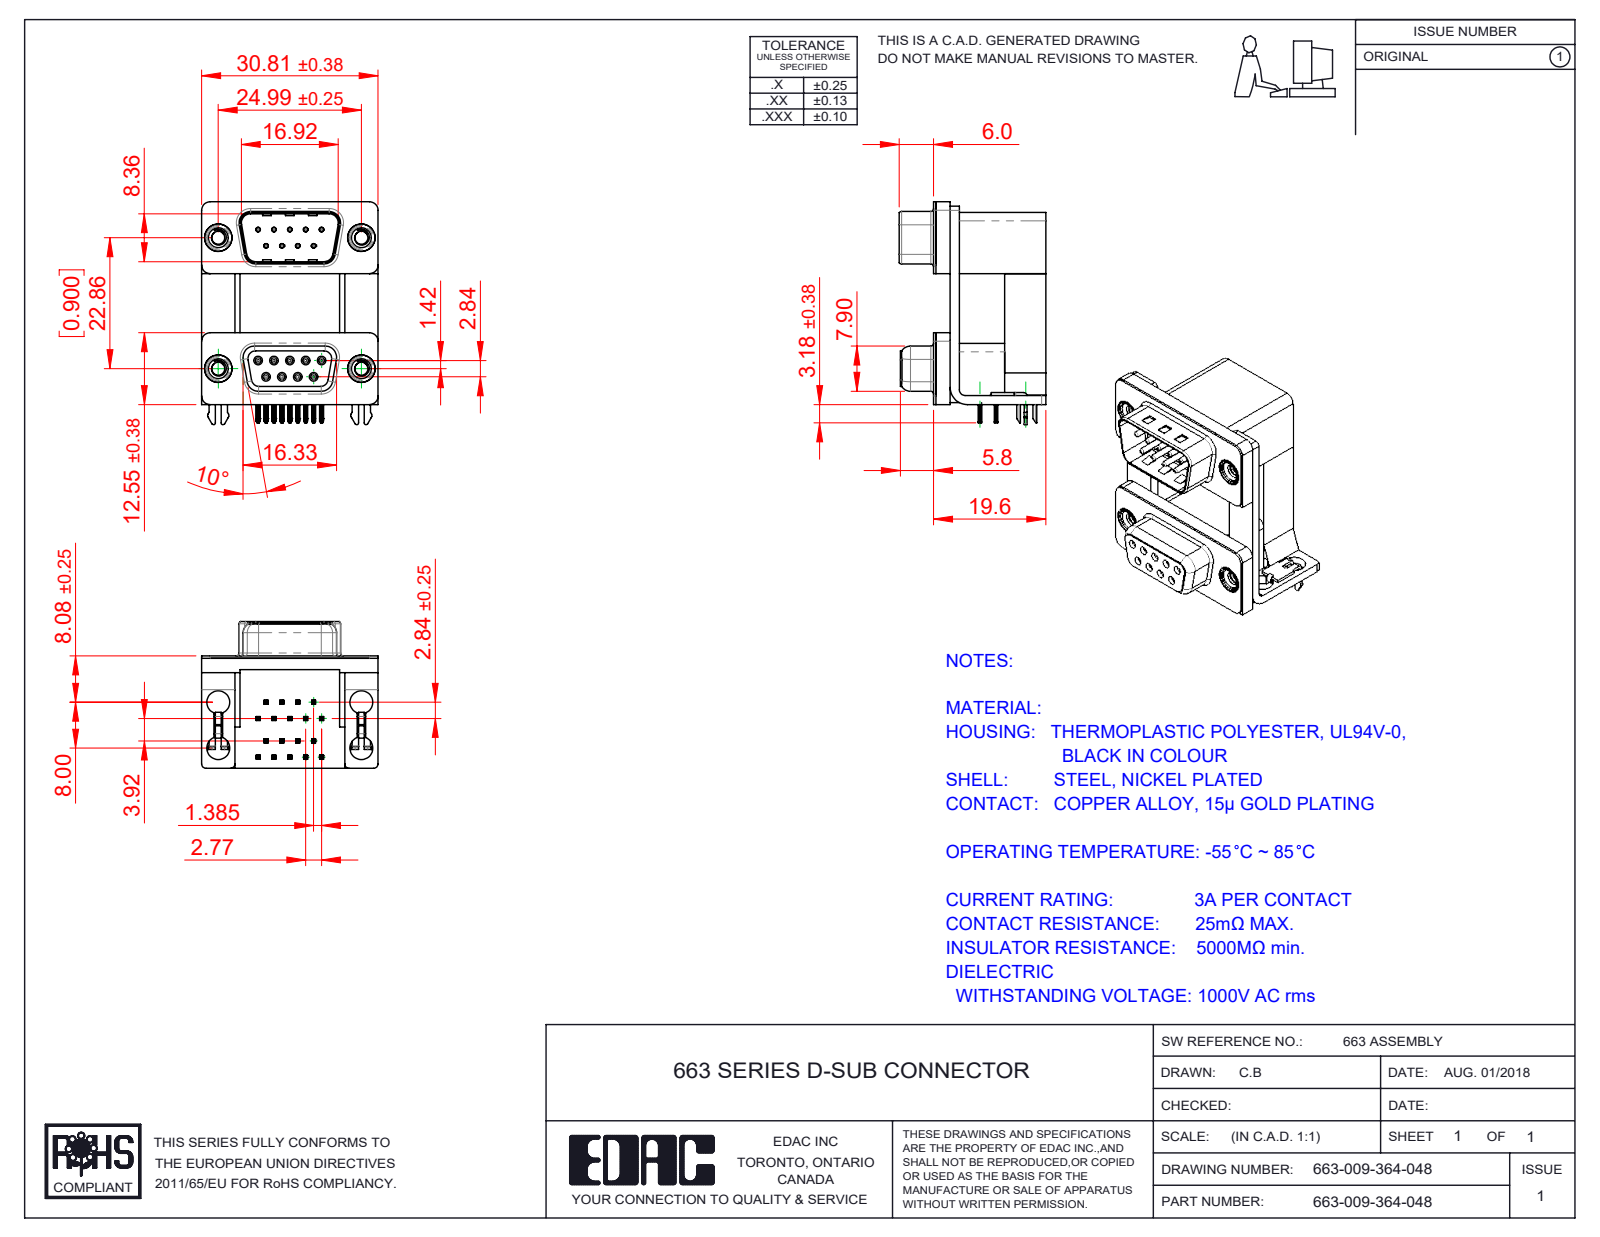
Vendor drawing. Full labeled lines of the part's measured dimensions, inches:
Part name (STEP PRODUCT): 663 Threaded Rivet_4-40; 663-009-364-048; 663 Housing Spacer_09 Contacts H; 663 Housing Lower_09 Contacts (+8 more)
STEP written by: SolidWorks 2020 (CONFIG_CONTROL_DESIGN)
Units: inches
Bodies: 31 solids, 2637 faces (1341 planar, 725 cylindrical, 571 other)
Overall size (bounding box): 1.532 × 1.213 × 1.008
Volume: 0.693 in³ · Surface area: 20.39 in²
Round holes (diameter × count): ⌀0.031 ×18, ⌀0.014 ×9, ⌀0.035 ×9, ⌀0.157 ×8, ⌀0.089 ×4, ⌀0.138 ×4, ⌀0.189 ×4, ⌀0.197 ×4
Round bosses / shafts (diameter × count): ⌀0.047 ×9, ⌀0.03 ×9, ⌀0.193 ×4, ⌀0.187 ×4, ⌀0.154 ×4
Partial cylindrical surfaces — rounded edges, fillets, slot ends (radius × count): R0.004 ×73, R0.01 ×42, R0.006 ×36, R0.005 ×18, R0.014 ×18, R0.02 ×16, R0.059 ×15, R0.03 ×10
Main face-to-face distances: 0.098, 0.016, 0.756, 0.657, 0.472, 0.283, 0.374, 0.063, 0.488, 0.772
Hole centre spacings: 0.124, 0.109, 0.907, 0.9, 0.218, 0.926, 0.79, 1.013
